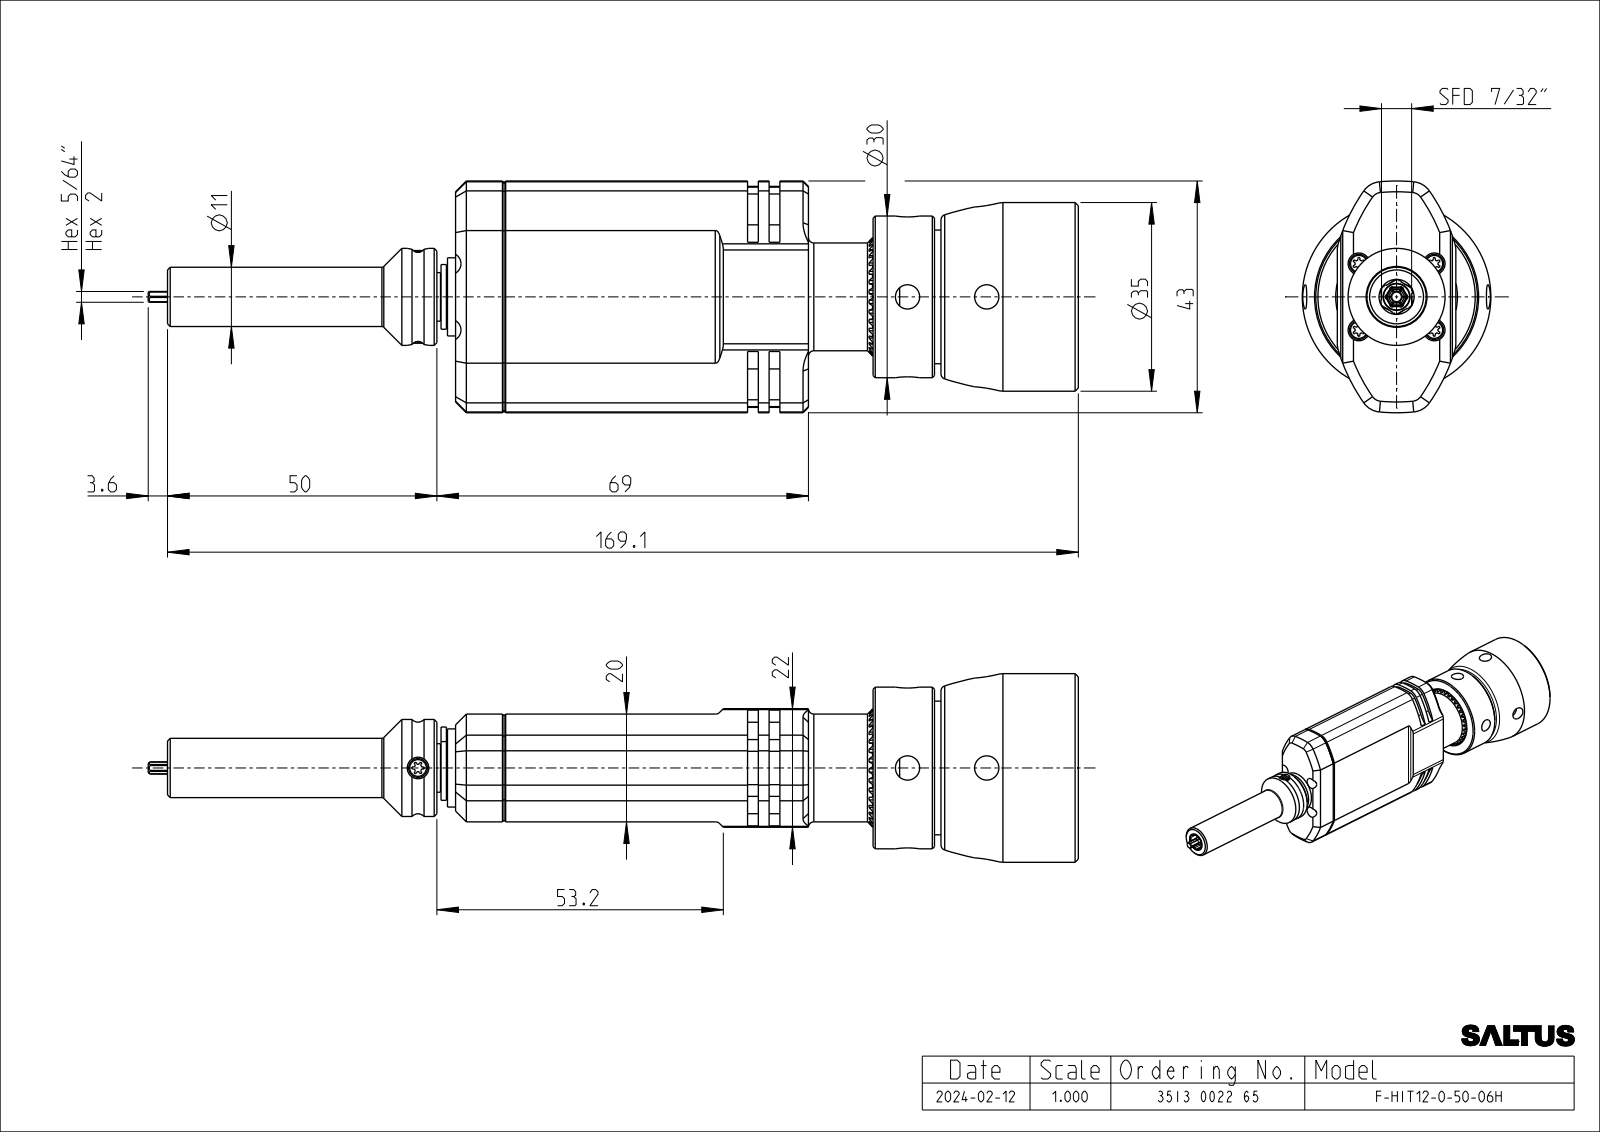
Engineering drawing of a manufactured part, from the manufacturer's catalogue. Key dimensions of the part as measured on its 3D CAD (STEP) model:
Part name (STEP PRODUCT): 3513002265_SW0001
STEP written by: CREO PARAMETRIC BY PTC INC, 2022414 (CONFIG_CONTROL_DESIGN)
Units: inches
Bodies: 1 solid, 1122 faces (383 planar, 416 cylindrical, 323 other)
Overall size (bounding box): 6.797 × 1.693 × 1.378
Volume: 5.601 in³ · Surface area: 30.68 in²
Round holes (diameter × count): ⌀0.157 ×5, ⌀0.177 ×4, ⌀0.047 ×2, ⌀0.358 ×1, ⌀0.866 ×1, ⌀0.992 ×1, ⌀1.043 ×1
Round bosses / shafts (diameter × count): ⌀0.138 ×5, ⌀1.378 ×1, ⌀1.181 ×1, ⌀1.024 ×1, ⌀0.976 ×1, ⌀0.933 ×1, ⌀0.795 ×1, ⌀0.787 ×1
Partial cylindrical surfaces — rounded edges, fillets, slot ends (radius × count): R0.008 ×42, R0.012 ×30, R0.039 ×18, R0.098 ×12, R0.157 ×8, R0.03 ×6, R1.299 ×6, R1.339 ×6
Main face-to-face distances: 0.787, 0.039, 0.827, 1.972, 4.551, 2.579, 0.866, 0.047, 1.5, 0.472
Hole centre spacings: 0.367, 0.176, 0.245, 0.317, 0.484, 0.537, 0.551, 0.579
